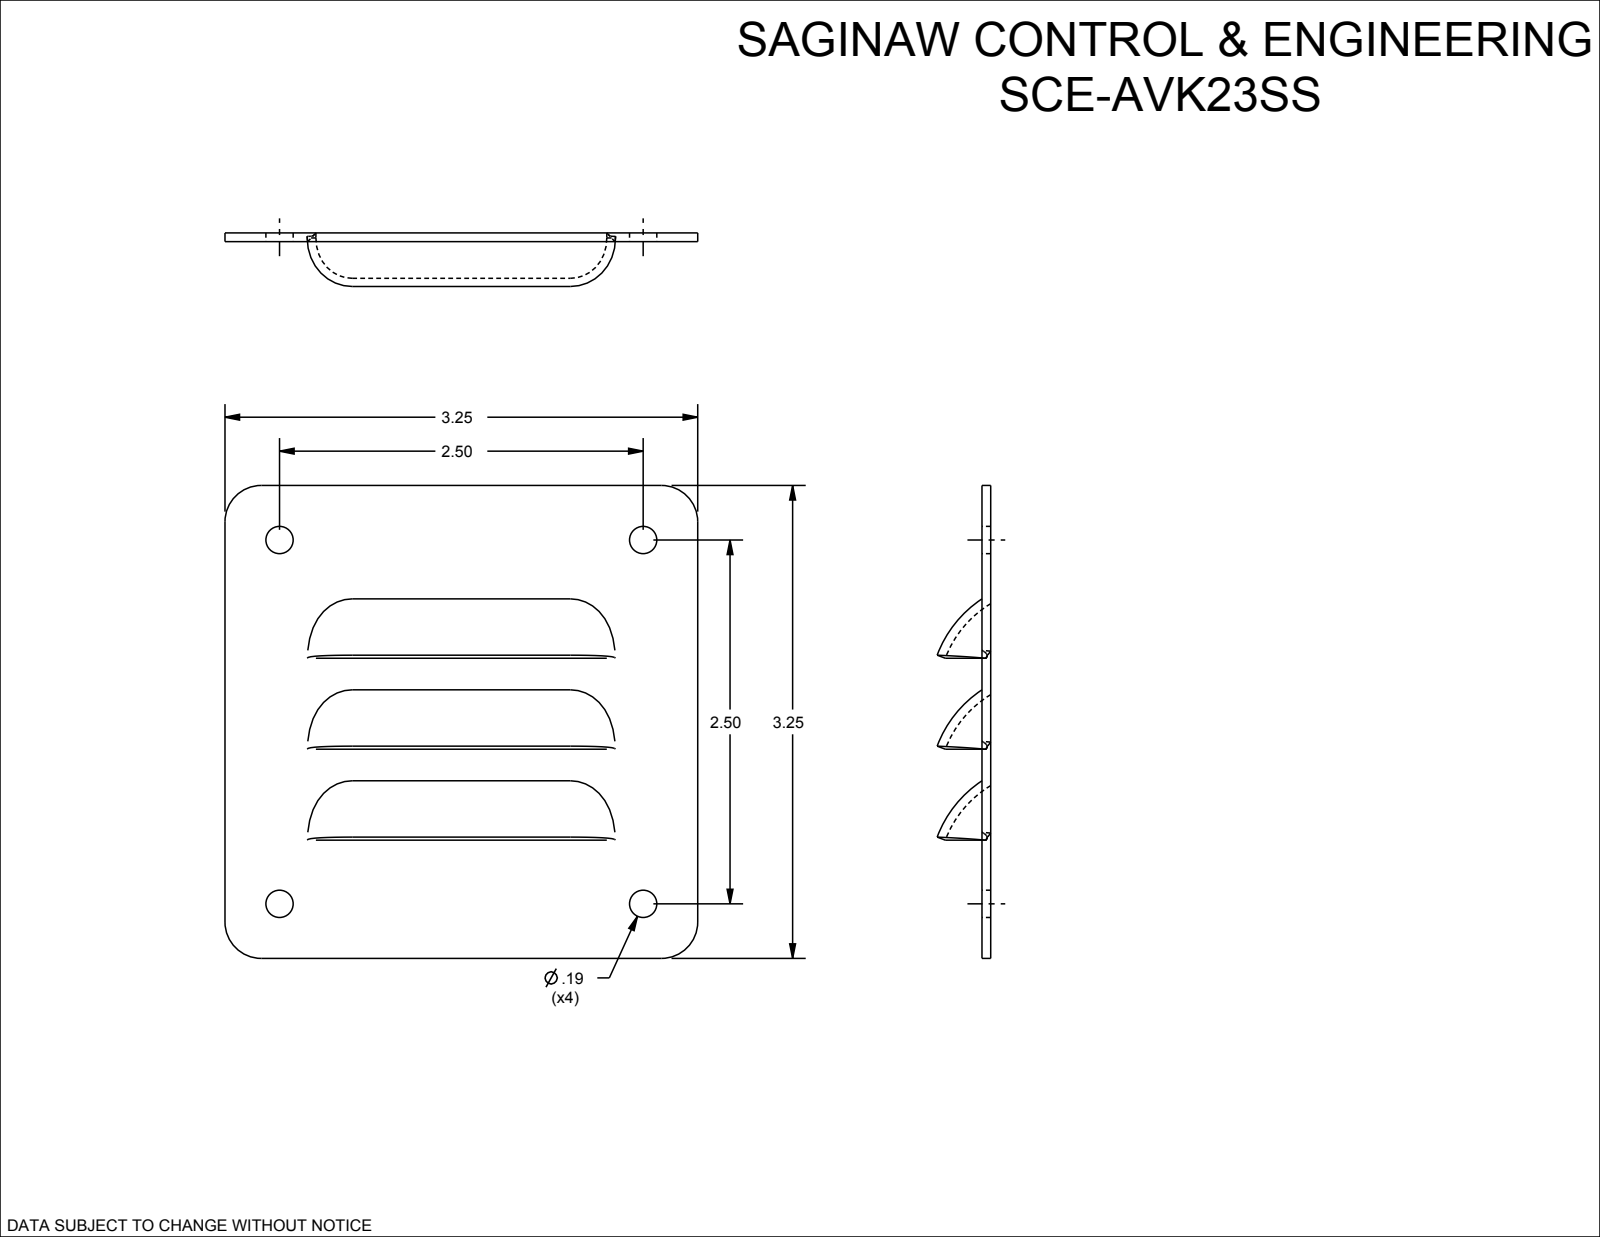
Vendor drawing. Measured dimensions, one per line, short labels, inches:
name: SCE-AVK23
written by: SolidWorks 2021 (AUTOMOTIVE_DESIGN)
unit: in
bodies: 1 solid, 57 faces (15 planar, 18 cylindrical, 24 other)
size: 3.25 × 3.25 × 0.467
volume: 0.681 in³; area: 24.3 in²
holes: 4× ⌀0.187
rounds: 4× R0.25, 3× R0.74, 3× R0.8
face distances: 0.06, 3.25, 0.625, 0.625, 1.25, 0.29, 0.96, 0.335, 1.437, 1.812
hole spacings: 2.5, 3.535
